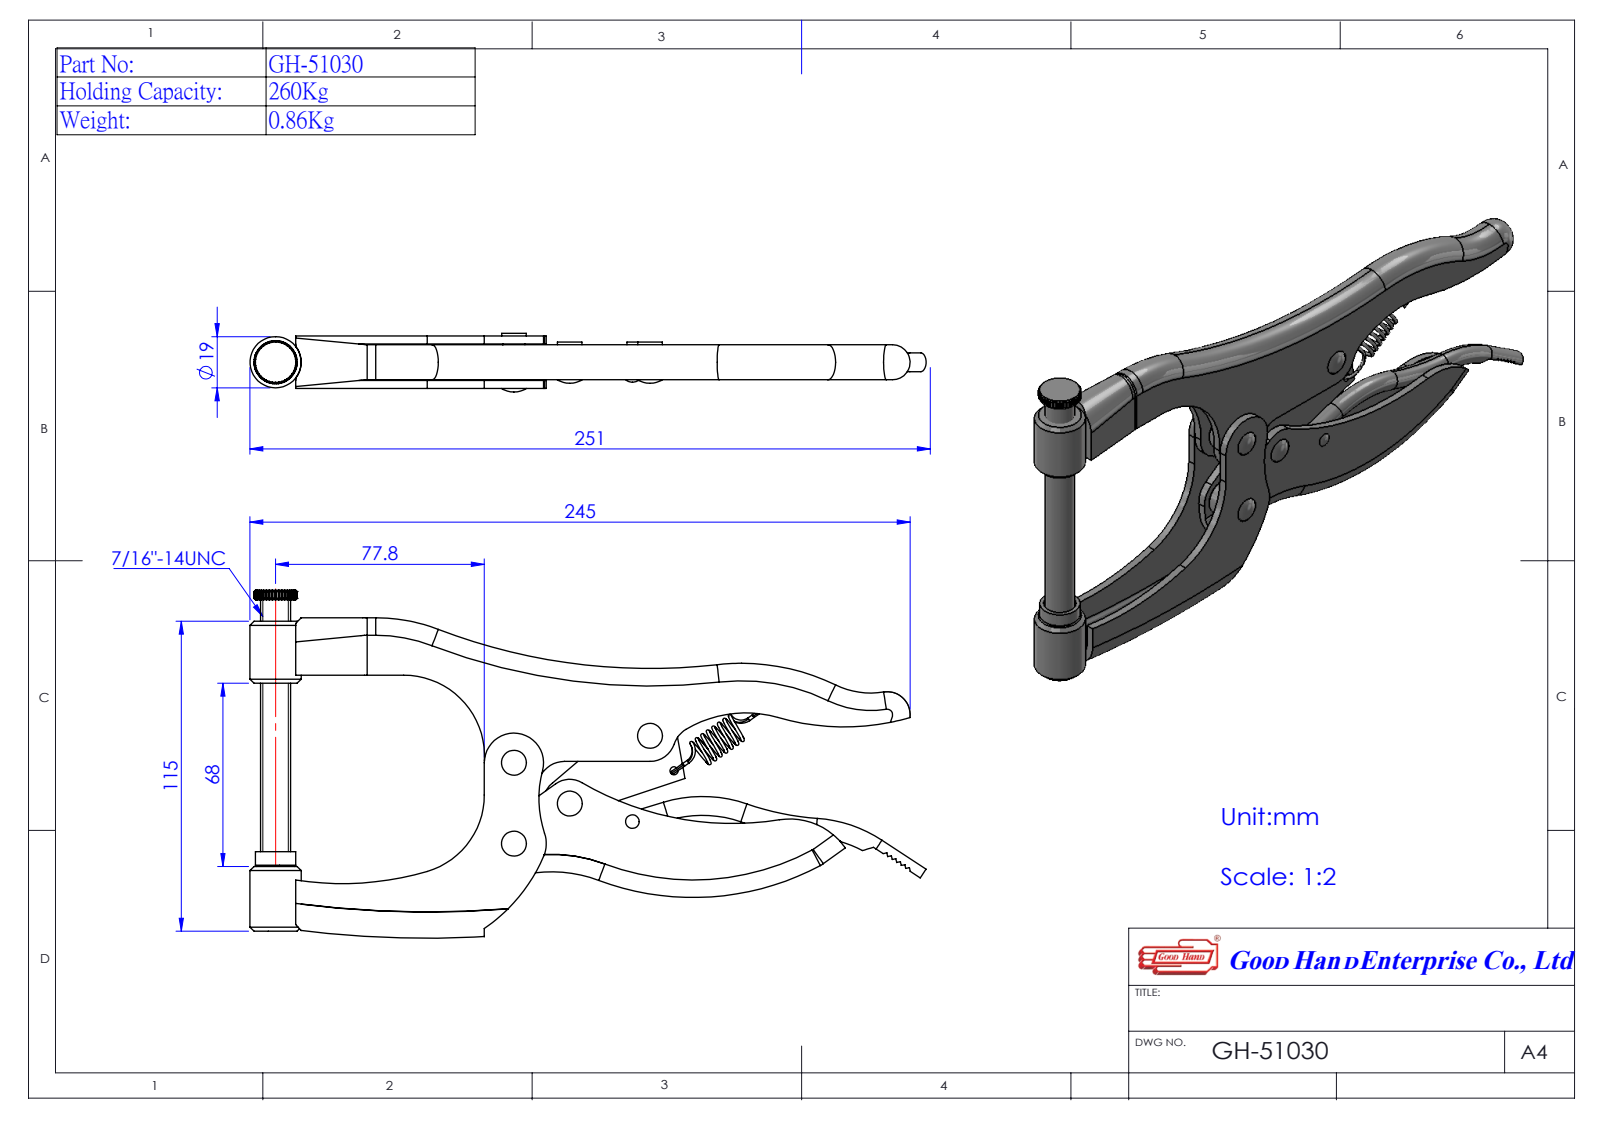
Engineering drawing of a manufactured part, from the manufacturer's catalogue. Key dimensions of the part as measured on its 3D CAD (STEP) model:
Part name (STEP PRODUCT): Group1^GH-51030(單一)-5; GH-51030(單一)-5
STEP written by: SolidWorks 2016 (AUTOMOTIVE_DESIGN)
Units: millimetres
Bodies: 5 solids, 484 faces (162 planar, 154 cylindrical, 168 other)
Overall size (bounding box): 251 × 130.59 × 21.8
Volume: 115 360 mm³ · Surface area: 71 290 mm²
Round holes (diameter × count): ⌀3.1 ×1, ⌀7 ×1
Round bosses / shafts (diameter × count): ⌀9.1 ×4, ⌀8.1 ×4, ⌀1.2 ×4, ⌀6 ×2, ⌀22 ×1, ⌀19 ×1, ⌀15 ×1, ⌀11.11 ×1
Partial cylindrical surfaces — rounded edges, fillets, slot ends (radius × count): R3.5 ×6, R10 ×6, R6.5 ×5, R9 ×2, R13 ×2, R2 ×1, R8 ×1, R9.5 ×1
Main face-to-face distances: 3, 10, 3.25, 13.25, 13, 7, 10.25, 6.25, 16.25, 16.5
